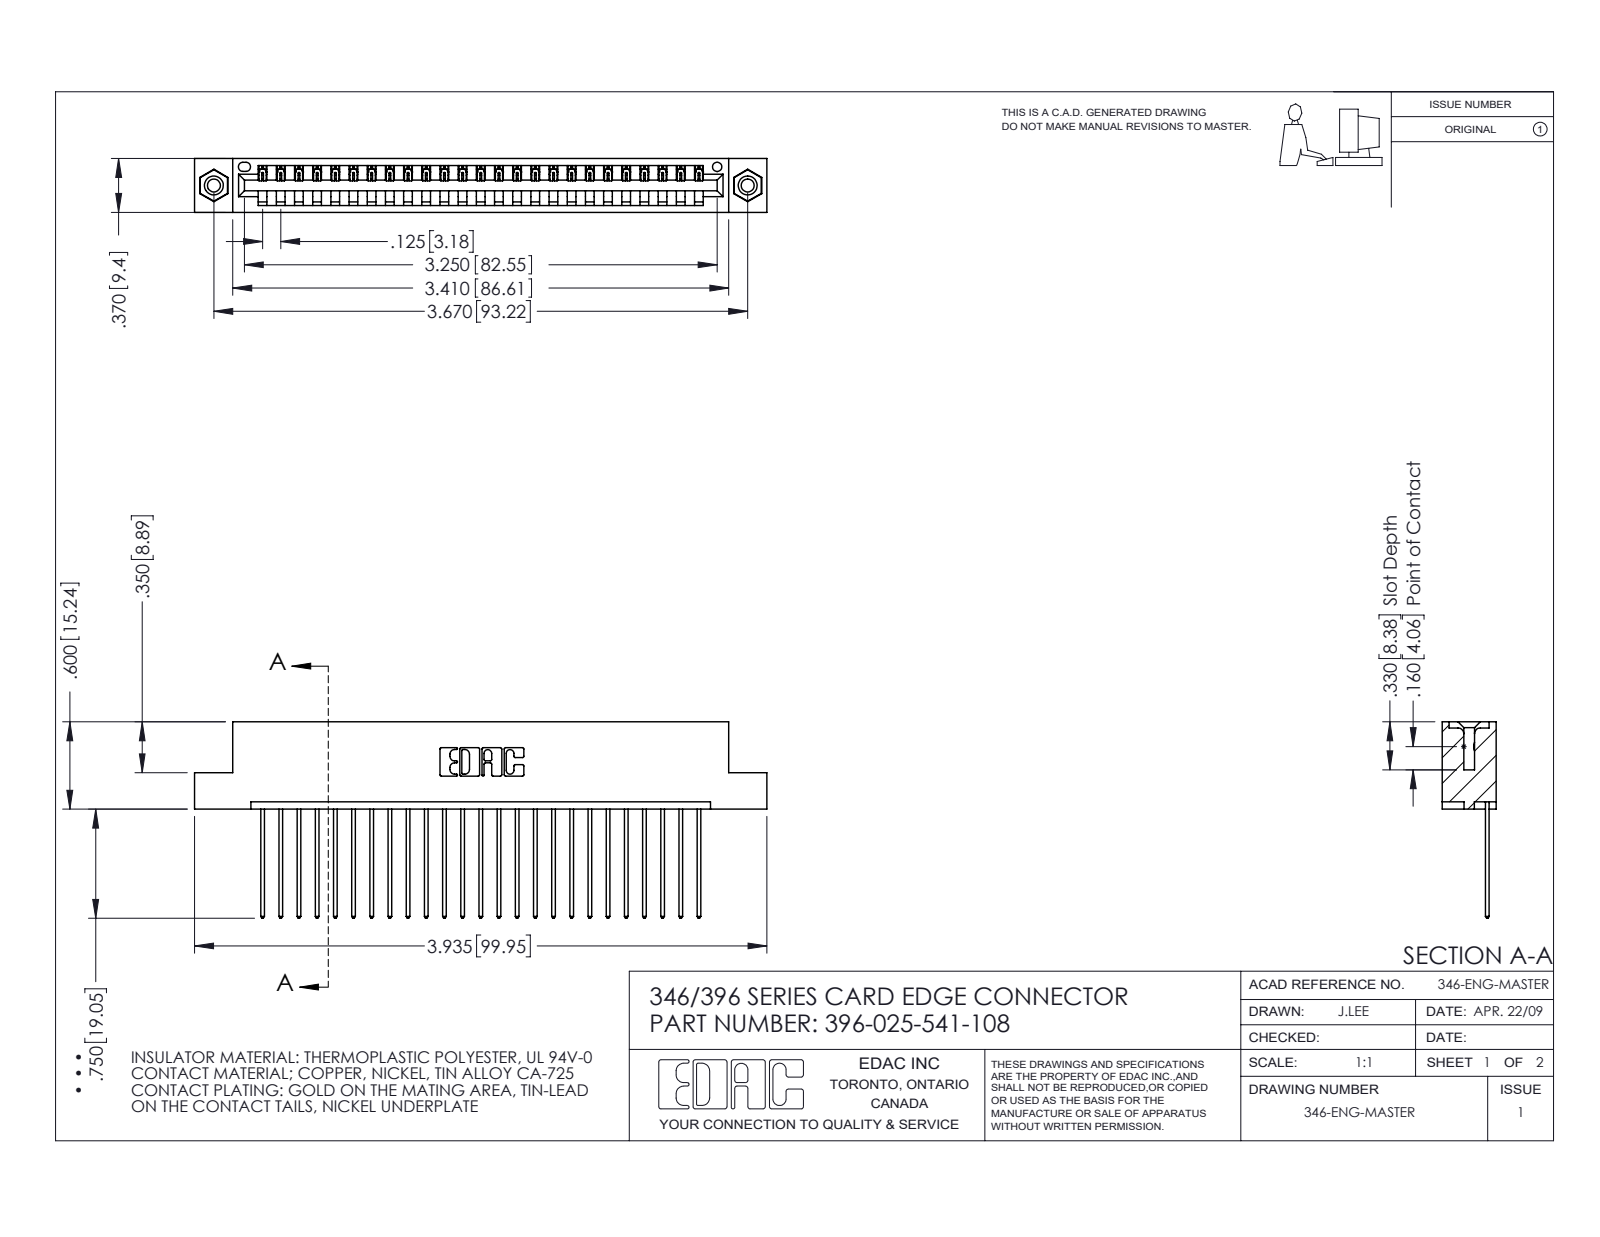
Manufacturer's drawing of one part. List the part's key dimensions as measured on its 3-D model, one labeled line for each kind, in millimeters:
Part name (STEP PRODUCT): 345-250-001_345-250-003-102; 345-292-001_345-293-141; 346 Part_Flush Mounting Lugs - 0.156 Dia-TI; 396-025-541-108
STEP written by: SolidWorks 2016 (CONFIG_CONTROL_DESIGN)
Units: millimetres
Bodies: 28 solids, 1632 faces (1108 planar, 508 cylindrical, 16 other)
Overall size (bounding box): 99.9 × 34.3 × 9.4
Volume: 9 520 mm³ · Surface area: 12 240 mm²
Round holes (diameter × count): ⌀2.3 ×2, ⌀3.2 ×2, ⌀4 ×2, ⌀1.6 ×1
Round bosses / shafts (diameter × count): ⌀3.9 ×2
Partial cylindrical surfaces — rounded edges, fillets, slot ends (radius × count): R0.2 ×50, R0.3 ×50, R0.3 ×22, R0.2 ×6, R0.8 ×6, R0.7 ×3, R0.8 ×2, R1 ×2
Main face-to-face distances: 1.2, 8.2, 9.4, 6.4, 1.8, 7.6, 0.6, 3.8, 5.6, 2.5
Hole centre spacings: 6.2, 87.9, 93.2
